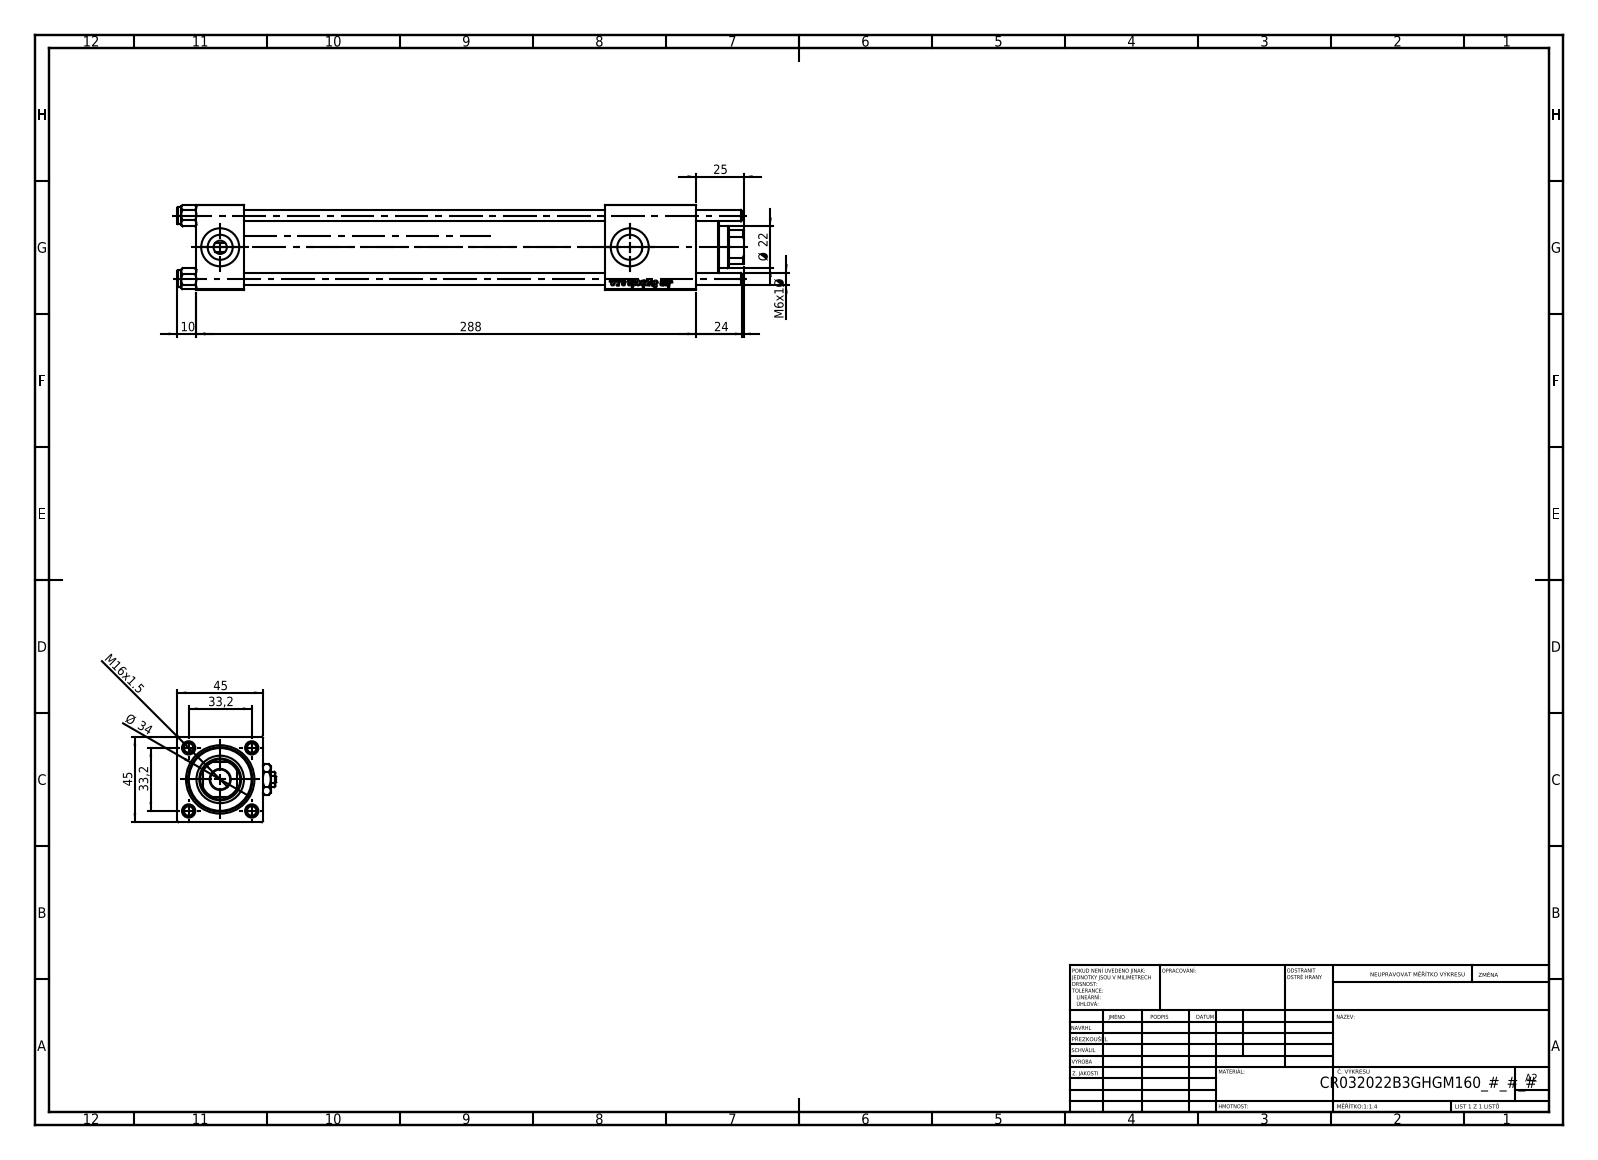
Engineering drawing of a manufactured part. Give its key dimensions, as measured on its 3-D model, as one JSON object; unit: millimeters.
{"part_name": "V215CR_B-1; V215CR_B_TYCINKA; V215_VC_A; V215CR_VCP_B (+2 more)", "step_written_by": "SolidWorks 2019 (CONFIG_CONTROL_DESIGN)", "units": "millimeters", "bodies": {"solids": 13, "faces": 1256, "planar": 478, "cylindrical": 88, "other": 690}, "overall_size": [298, 52, 45], "volume_mm3": 328014, "surface_area_mm2": 129649, "round_holes": [[6, 4], [7, 2], [13.16, 2], [20, 2], [10.5, 1], [22, 1], [24, 1], [25, 1], [32, 1], [33, 1]], "round_bosses_or_shafts": [[9, 4], [38, 1], [34, 1]], "partial_cylinders_radius": [[10.5, 1]], "face_to_face_distances": [45, 25, 263, 215, 190, 44.8, 238, 48, 234.3, 209.3], "hole_center_spacings": [23.48, 33.2, 46.95, 215.5]}
